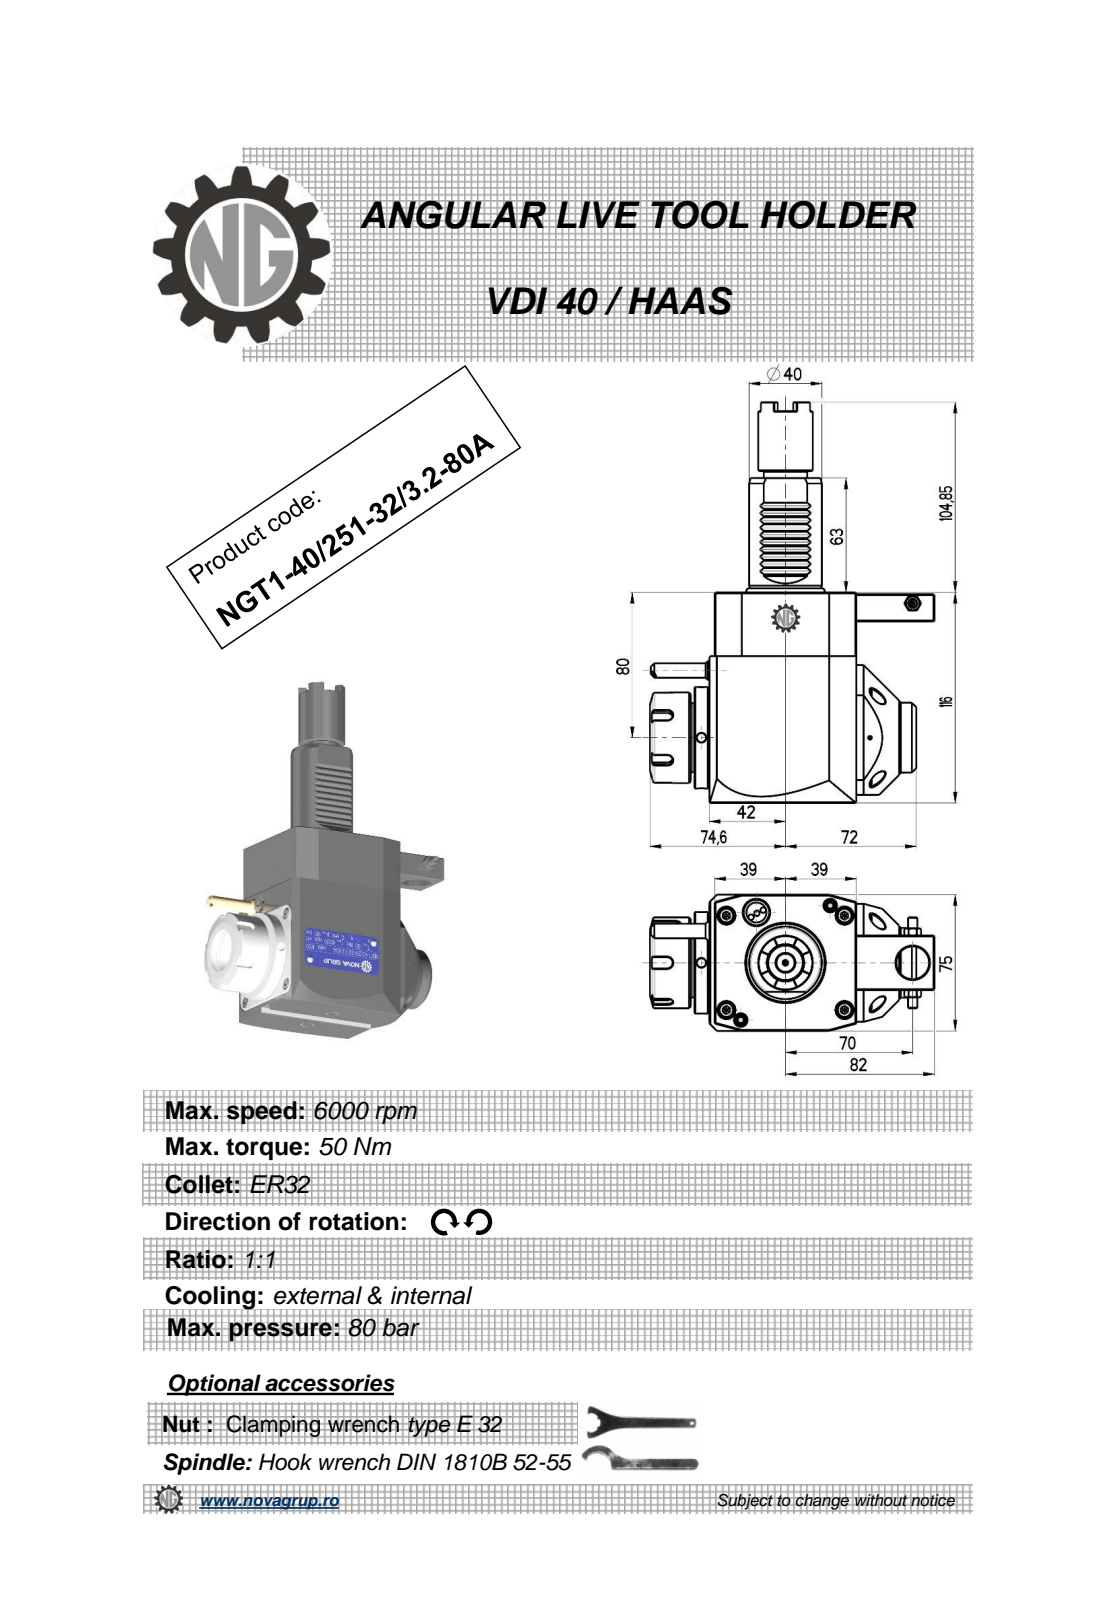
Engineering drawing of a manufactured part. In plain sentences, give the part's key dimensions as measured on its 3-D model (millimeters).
The part is named "NGT1_40_251_32_3_2_80A". Its 3-D file was written by "PRO/ENGINEER BY PARAMETRIC TECHNOLOGY CORPORATION, 2010280 (CONFIG_CONTROL_DESIGN)". It is 1 solid with 453 faces: 216 planar, 91 cylindrical and 146 other. Overall it measures 220.85 by 156.6 by 75 millimeters. Its volume is 942 170 cubic millimeters and its surface area 78 471 square millimeters. Round holes: 3 of diameter 5, 1 of diameter 3, 1 of diameter 4.2, 1 of diameter 9.5, 1 of diameter 18, 1 of diameter 27. Round bosses or shafts: 1 of diameter 56, 1 of diameter 50, 1 of diameter 43, 1 of diameter 40, 1 of diameter 38.5, 1 of diameter 30, 1 of diameter 24, 1 of diameter 10. Partial cylindrical surfaces (rounded edges, fillets, slot ends): 12 of radius 0.26, 10 of radius 0.3, 6 of radius 0.2, 5 of radius 3, 1 of radius 0.5, 1 of radius 10, 1 of radius 40. The main face-to-face distances are 75, 116, 81, 78, 3, 111, 1, 2.8, 80.8, 22.5. The hole center spacings are 39.58, 40.93, 72.5, 116.25, 137.8.
